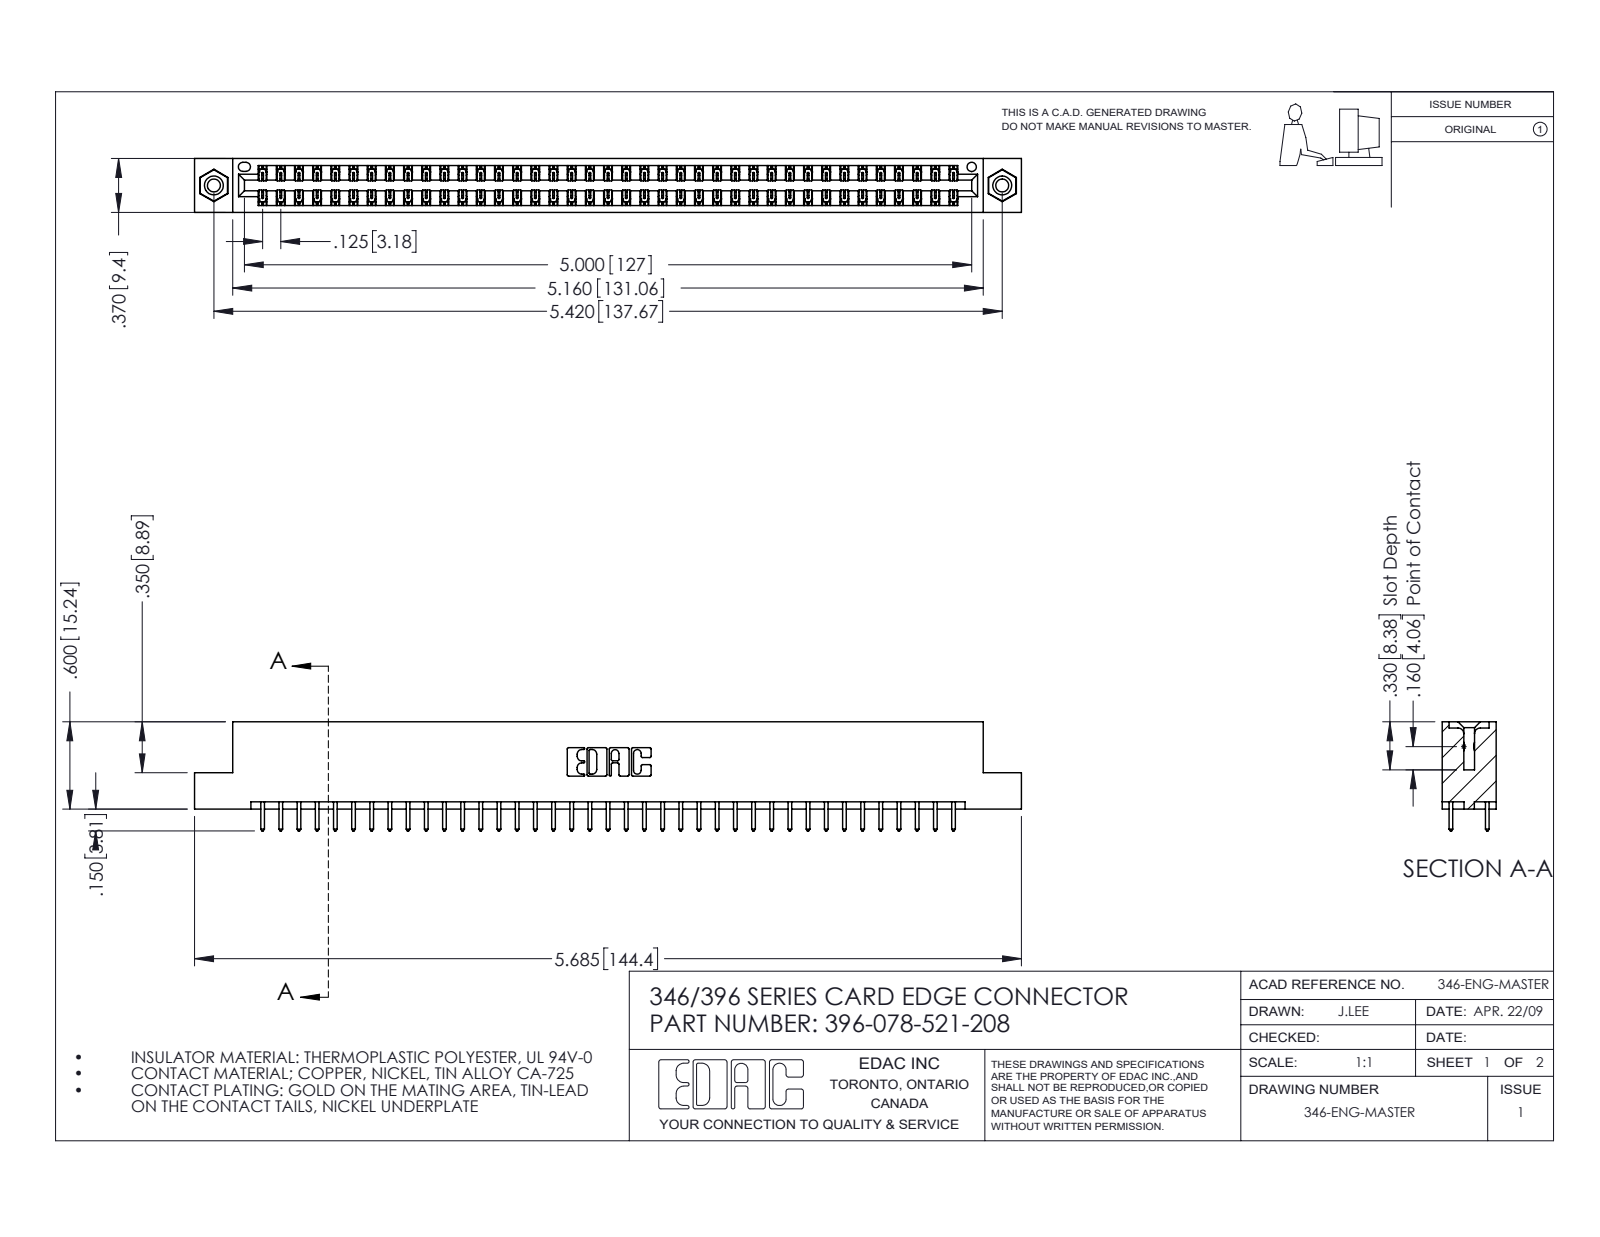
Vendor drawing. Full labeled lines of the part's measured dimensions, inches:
Part name (STEP PRODUCT): 396-078-521-208; 345-292-001_345-293-121; 345-250-001_345-250-003-102; 346 Part_Flush Mounting Lugs - 0.156 Dia-TI
STEP written by: SolidWorks 2016 (CONFIG_CONTROL_DESIGN)
Units: inches
Bodies: 81 solids, 4238 faces (2838 planar, 1384 cylindrical, 16 other)
Overall size (bounding box): 5.685 × 0.75 × 0.37
Volume: 0.855 in³ · Surface area: 29.49 in²
Round holes (diameter × count): ⌀0.089 ×2, ⌀0.125 ×2, ⌀0.156 ×2, ⌀0.064 ×1
Round bosses / shafts (diameter × count): ⌀0.155 ×2
Partial cylindrical surfaces — rounded edges, fillets, slot ends (radius × count): R0.006 ×117, R0.01 ×78, R0.01 ×22, R0.007 ×6, R0.031 ×6, R0.026 ×3, R0.014 ×2, R0.022 ×2
Main face-to-face distances: 0.048, 0.322, 0.25, 0.37, 0.072, 0.298, 0.025, 0.275, 0.148, 0.222
Hole centre spacings: 0.246, 5.211, 5.42
